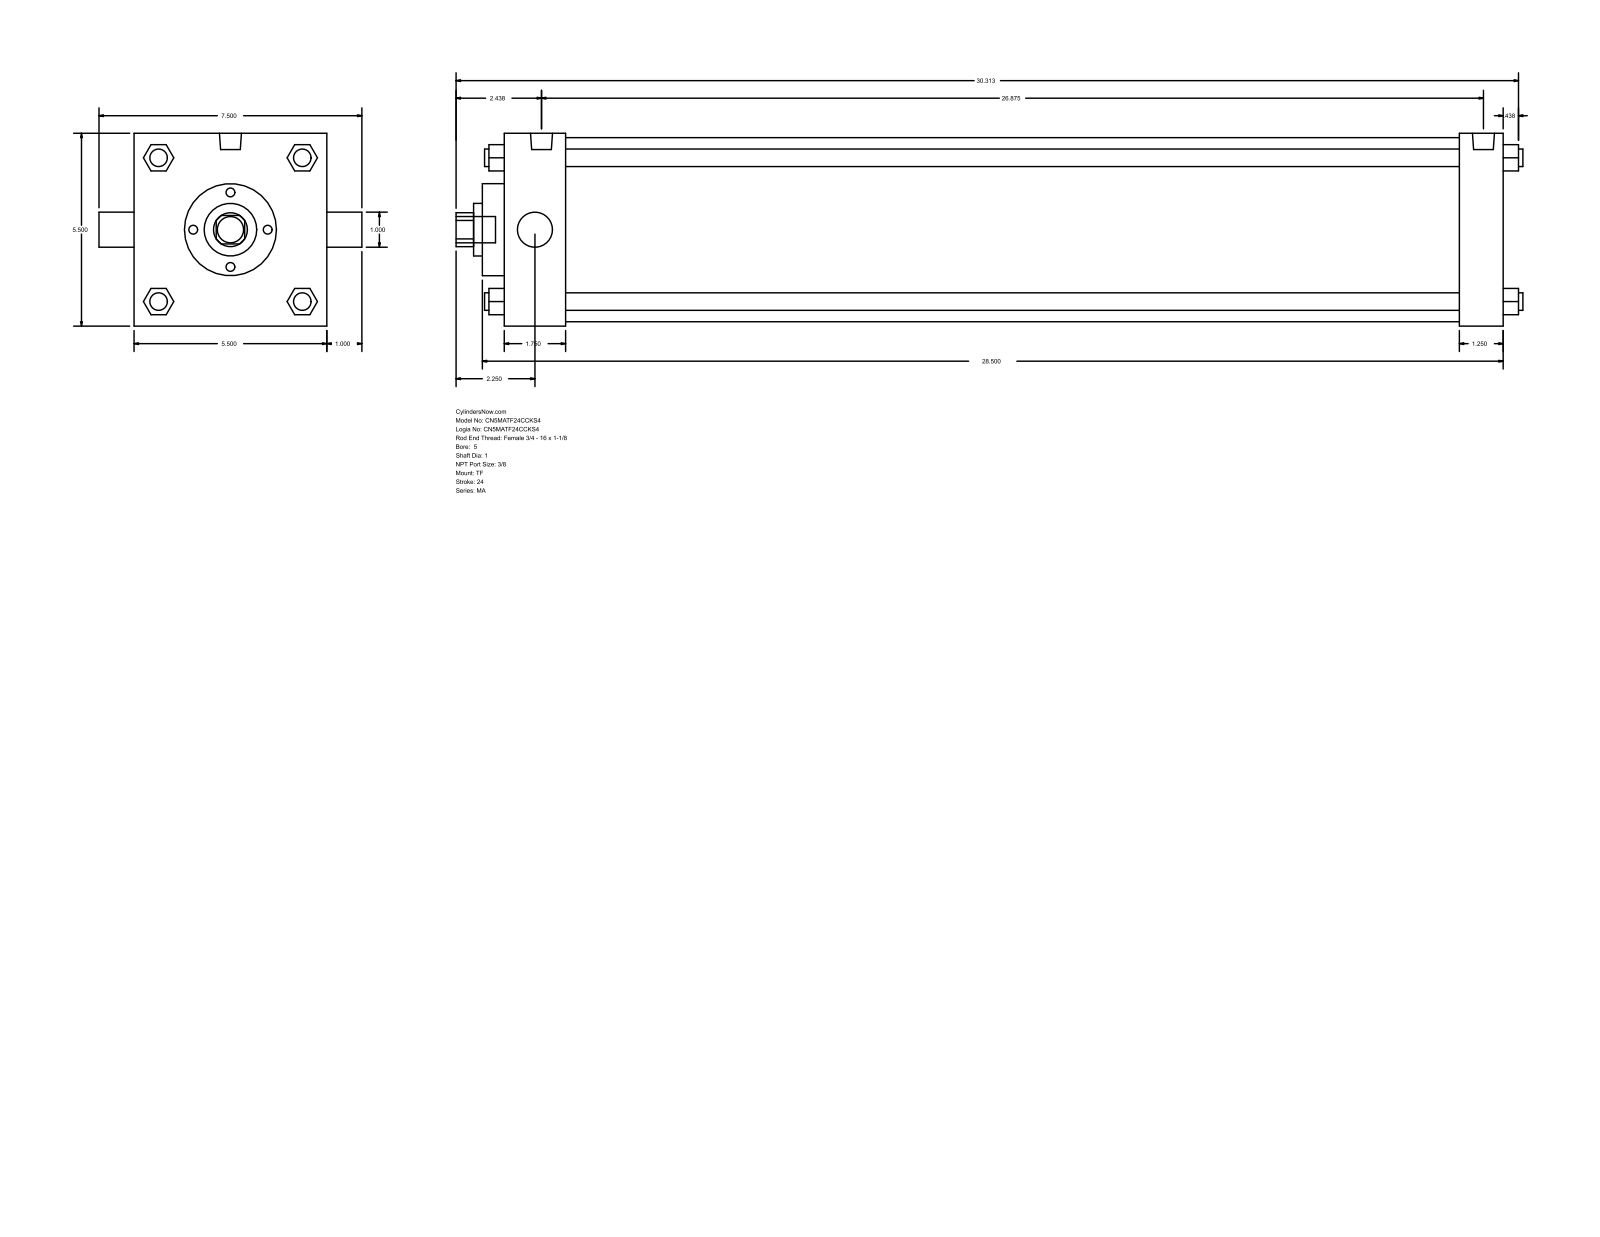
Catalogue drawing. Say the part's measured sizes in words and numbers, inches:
The part is named "MA_TF__0500_1". Its 3-D file was written by "GSSL Pune (CONFIG_CONTROL_DESIGN)". It is 0 solids with 122 faces: 93 planar, 29 cylindrical and 0 other. Overall it measures 30.437 by 7.5 by 5.5 inches. Round holes: 2 of diameter 1, 1 of diameter 1.5, 1 of diameter 2.625, 1 of diameter 5.25. Round bosses or shafts: 4 of diameter 0.5, 3 of diameter 0.437, 2 of diameter 0.627, 1 of diameter 0.75. Partial cylindrical surfaces (rounded edges, fillets, slot ends): 1 of radius 0.484. The main face-to-face distances are 5.5, 28.5, 27.25, 1.25, 1.75, 25.5, 26.75, 0.625, 2.375, 27.875.
